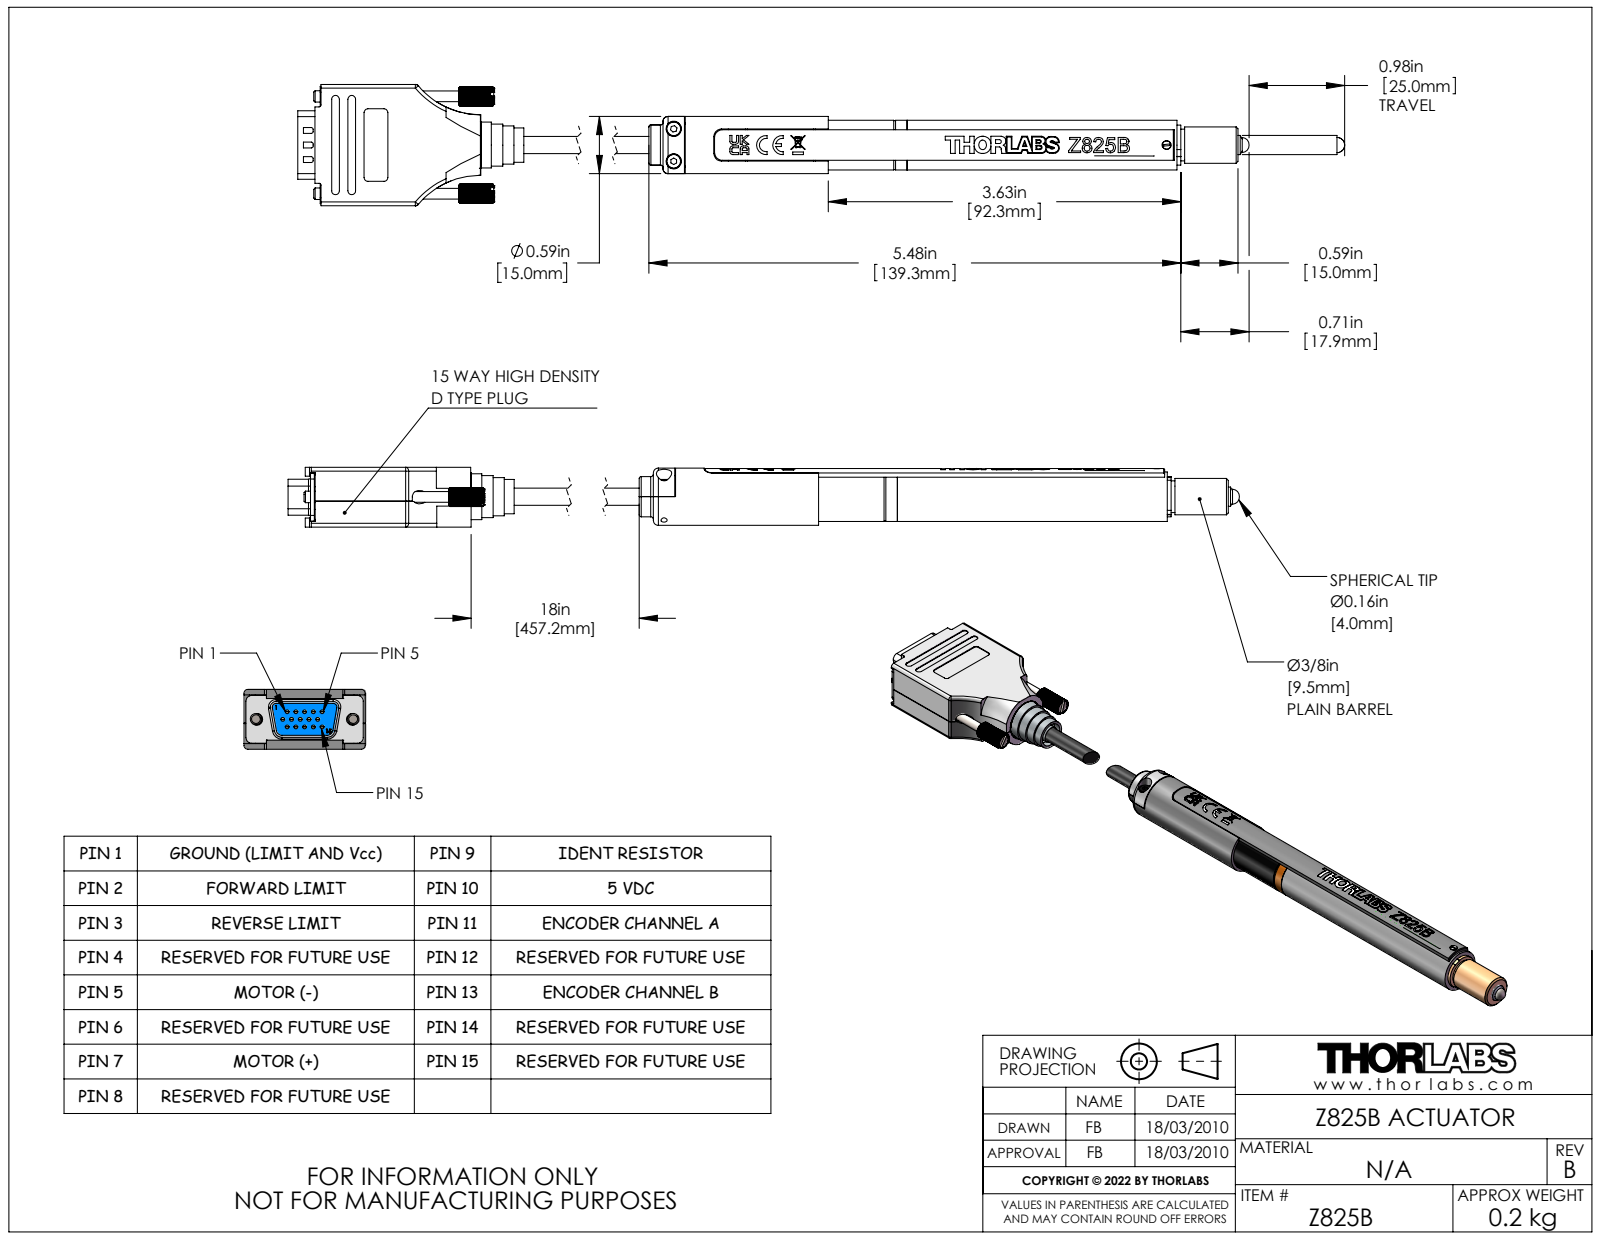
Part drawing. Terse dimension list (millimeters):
name: DB0389 - M2X8 Slt Cheesehead; 136060 - Ball End insert; 136010 - Cable Clamp; DA0017 - M1.2x 3 Csk Slt (+8 more)
written by: SolidWorks 2022 (CONFIG_CONTROL_DESIGN)
unit: mm
bodies: 24 solids, 1167 faces (628 planar, 388 cylindrical, 151 other)
size: 157.22 × 15 × 15
volume: 17 902 mm³; area: 19 656 mm²
holes: 4× ⌀1.6, 4× ⌀2.1, 3× ⌀0.95, 2× ⌀1.2, 2× ⌀2.7, 2× ⌀4, 1× ⌀0.47, 1× ⌀1.5, 1× ⌀1.7, 1× ⌀3, 1× ⌀3.1, 1× ⌀3.8
bosses: 4× ⌀2, 3× ⌀2.2, 2× ⌀3.8, 2× ⌀1.2, 2× ⌀0.8, 2× ⌀0.6, 1× ⌀15, 1× ⌀13
rounds: 21× R0.5, 8× R0.17, 8× R2, 4× R1, 4× R2.05, 2× R0.15, 2× R0.29, 2× R0.41
face distances: 1, 7, 1.16, 6.7, 0.86, 1.15, 6.85, 6.84, 5.84, 48.6
hole spacings: 4.75, 89.2, 124.87, 129.17, 4.3, 8.5, 9.5, 19.2
